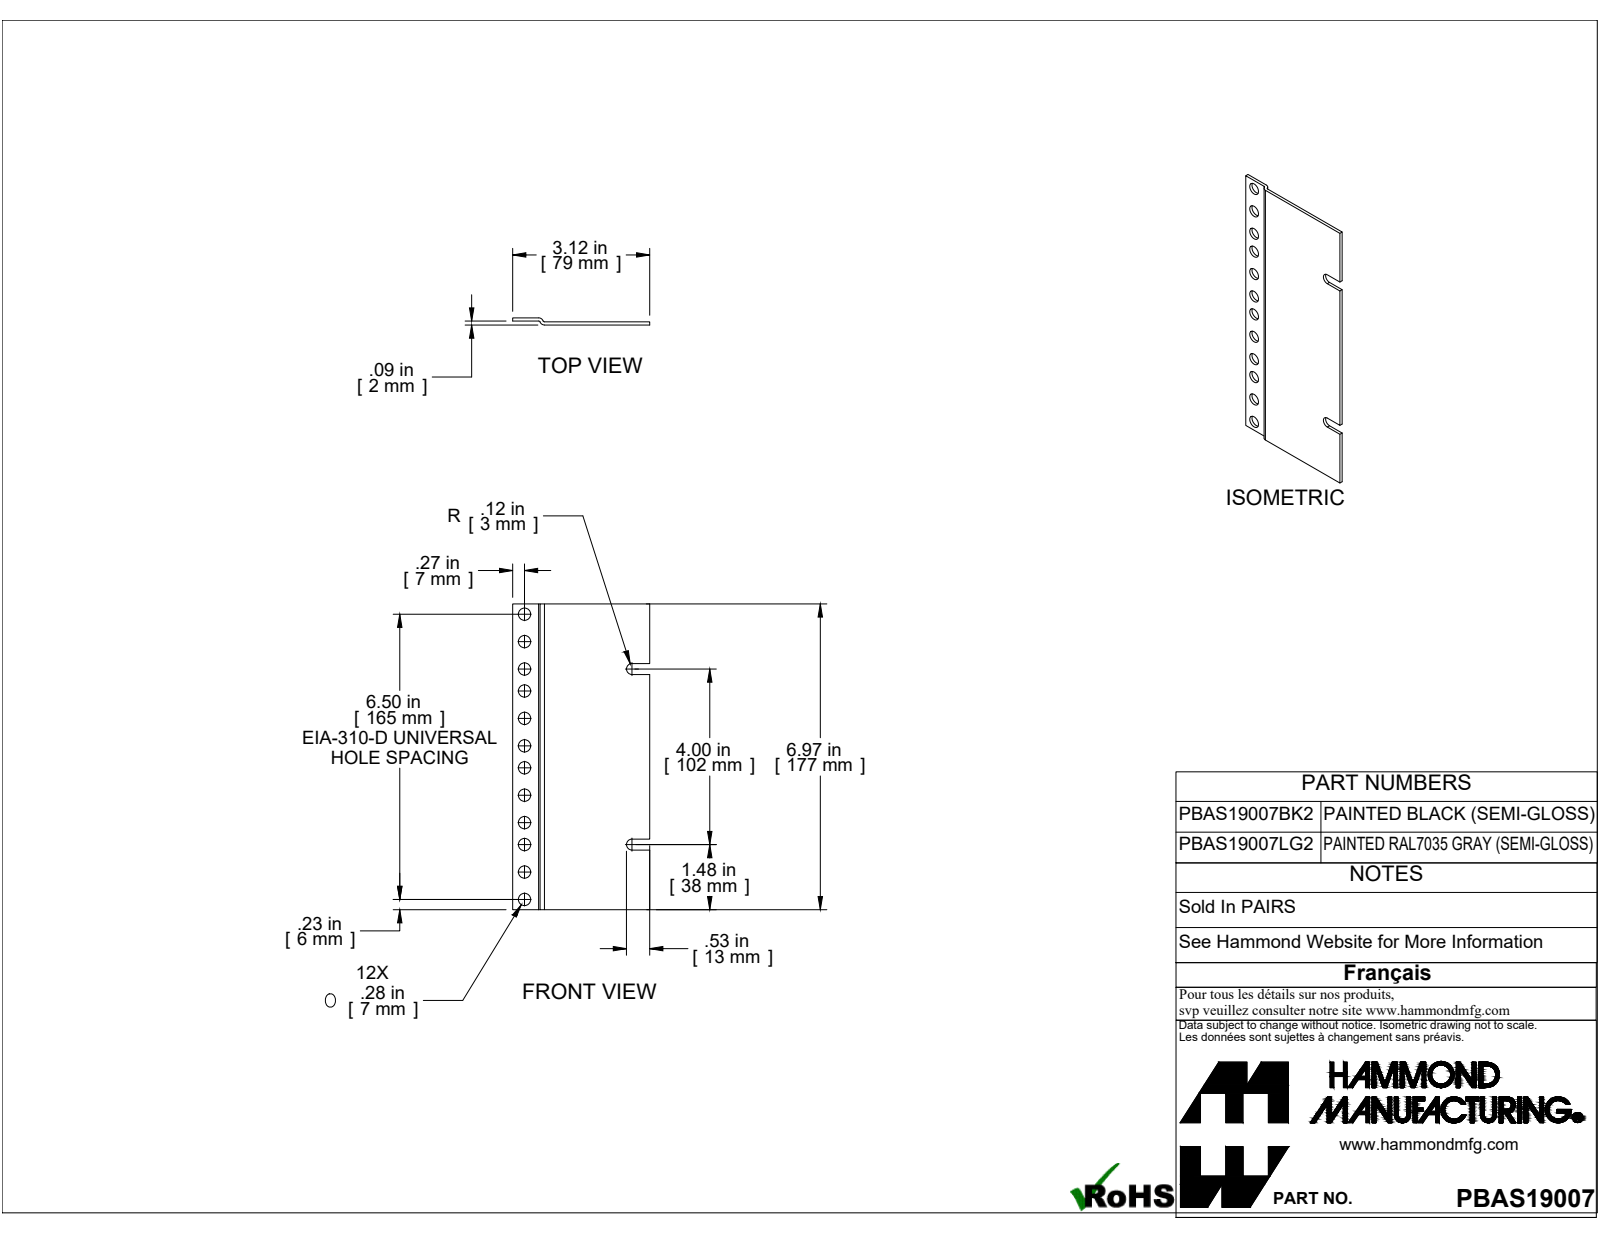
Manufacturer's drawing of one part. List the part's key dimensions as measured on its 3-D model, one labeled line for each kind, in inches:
Part name (STEP PRODUCT): PBAS19007LG2
STEP written by: SolidWorks 2019 (CONFIG_CONTROL_DESIGN)
Units: inches
Bodies: 1 solid, 32 faces (14 planar, 18 cylindrical, 0 other)
Overall size (bounding box): 6.968 × 3.125 × 0.162
Volume: 1.515 in³ · Surface area: 44.44 in²
Round holes (diameter × count): ⌀0.281 ×12
Partial cylindrical surfaces — rounded edges, fillets, slot ends (radius × count): R0.036 ×2, R0.108 ×2, R0.125 ×2
Main face-to-face distances: 0.072, 0.09, 0.162, 0.018, 0.09, 0.072, 3.125, 6.968, 1.359, 5.609
Hole centre spacings: 1.75, 0.625, 0.625, 1.125, 1.25, 2.375, 2.875, 3.5
